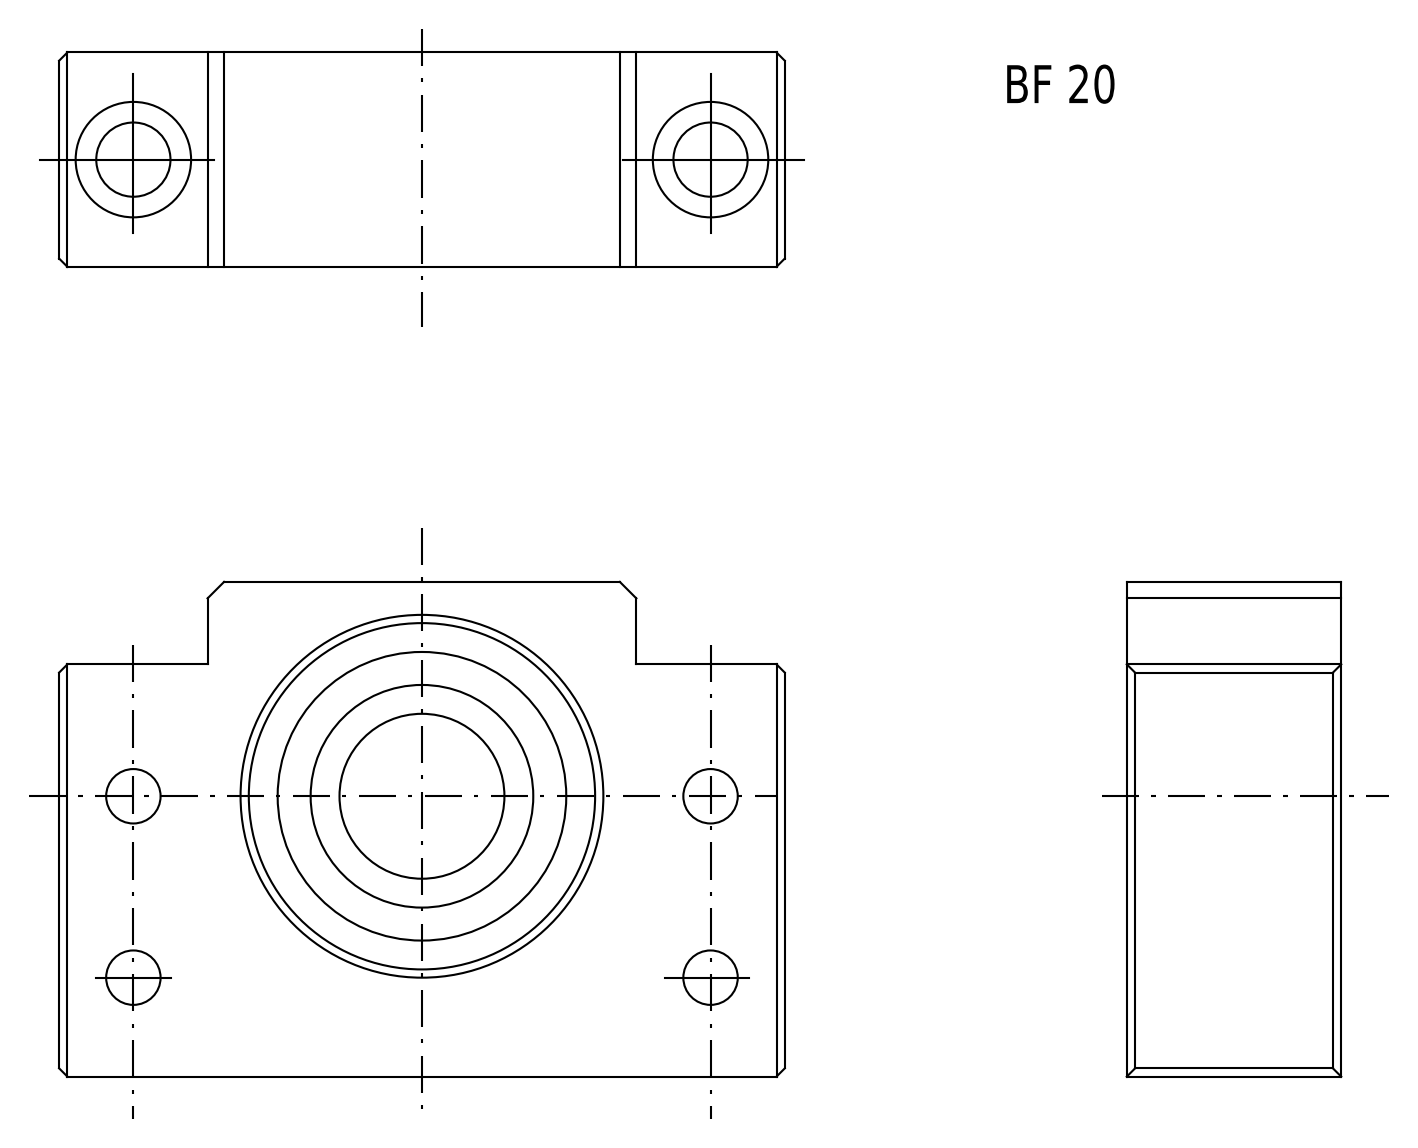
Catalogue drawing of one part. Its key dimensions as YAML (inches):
part_name: "BF20組合件"
step_written_by: "SolidWorks 2008 (CONFIG_CONTROL_DESIGN)"
units: inches
bodies: {solids: 17, faces: 162, planar: 50, cylindrical: 38, other: 74}
overall_size: [3.465, 2.362, 1.024]
volume: 5.438
surface_area: 44.89
round_holes:
  - {diameter: 0.26, count: 4}
  - {diameter: 0.354, count: 2}
  - {diameter: 0.551, count: 2}
  - {diameter: 0.787, count: 1}
  - {diameter: 1.457, count: 1}
  - {diameter: 1.654, count: 1}
round_bosses_or_shafts:
  - {diameter: 0.984, count: 1}
face_to_face_distances: [1.024, 2.362, 3.465, 0.276, 0.748, 1.969, 0.394, 0.709, 2.756, 0.472]
hole_center_spacings: [2.756, 0.866, 1.378, 1.628, 2.889]
